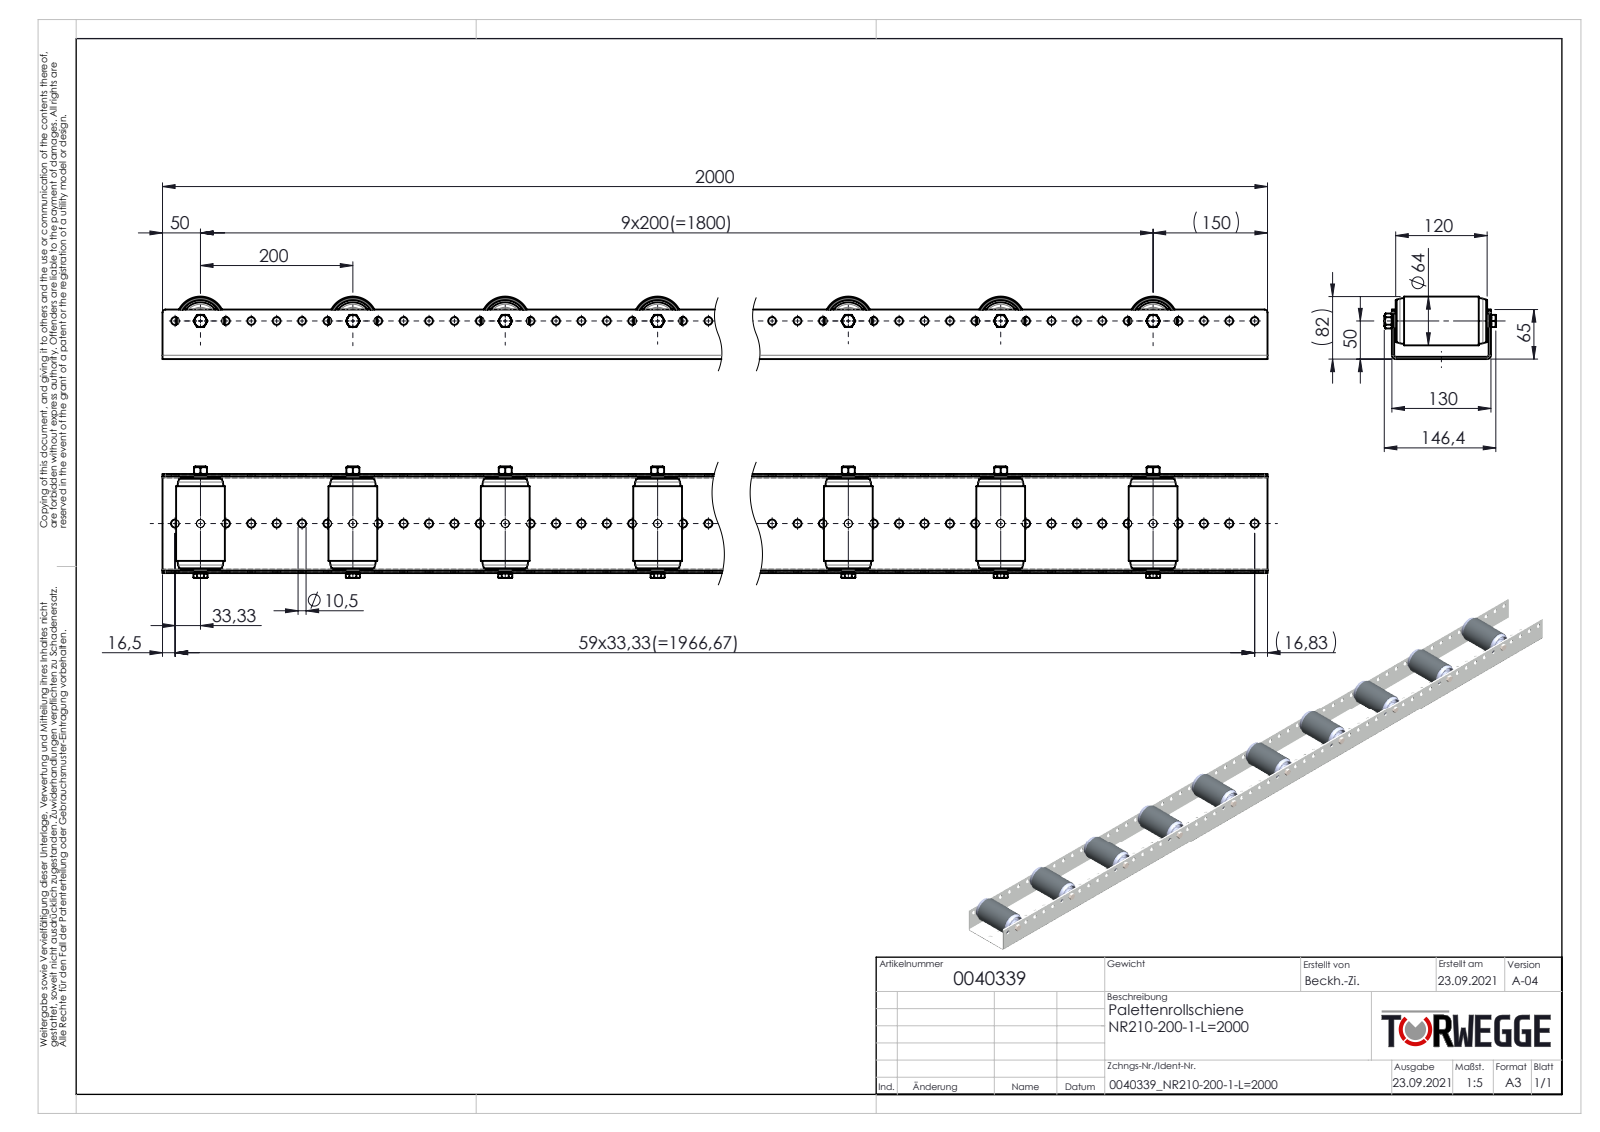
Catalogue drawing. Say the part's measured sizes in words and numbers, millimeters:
The part is named "hex bolt gradeab_din_ISO 4014 - M10 x 100 x 26-N; 0045587_U-65-130-65x3-(2M)_Schienenprofil-NR200-1_KFG_0045587 L=2000; K0024322_NR-210-60-10-PVC2mm; 0046710_Sechskantmutter_DIN980_M10 (+1 more)". Its 3-D file was written by "SolidWorks 2020 (AUTOMOTIVE_DESIGN)". It is 21 solids with 1676 faces: 368 planar, 688 cylindrical and 620 other. Overall it measures 2000 by 146.4 by 82 millimeters. Its volume is 1 572 000 cubic millimeters and its surface area 1 625 000 square millimeters. Round holes: 60 of diameter 10.2, 60 of diameter 10.5, 10 of diameter 8.38, 10 of diameter 49. Round bosses or shafts: 10 of diameter 64, 10 of diameter 60, 10 of diameter 55, 10 of diameter 30, 10 of diameter 24, 10 of diameter 16, 10 of diameter 10. Partial cylindrical surfaces (rounded edges, fillets, slot ends): 2 of radius 2, 2 of radius 4, 2 of radius 5. The main face-to-face distances are 3, 127, 130, 124, 65, 62, 16, 13, 114, 111. The hole center spacings are 100, 200, 300, 33.33, 66.67, 400, 133.33, 166.67.
